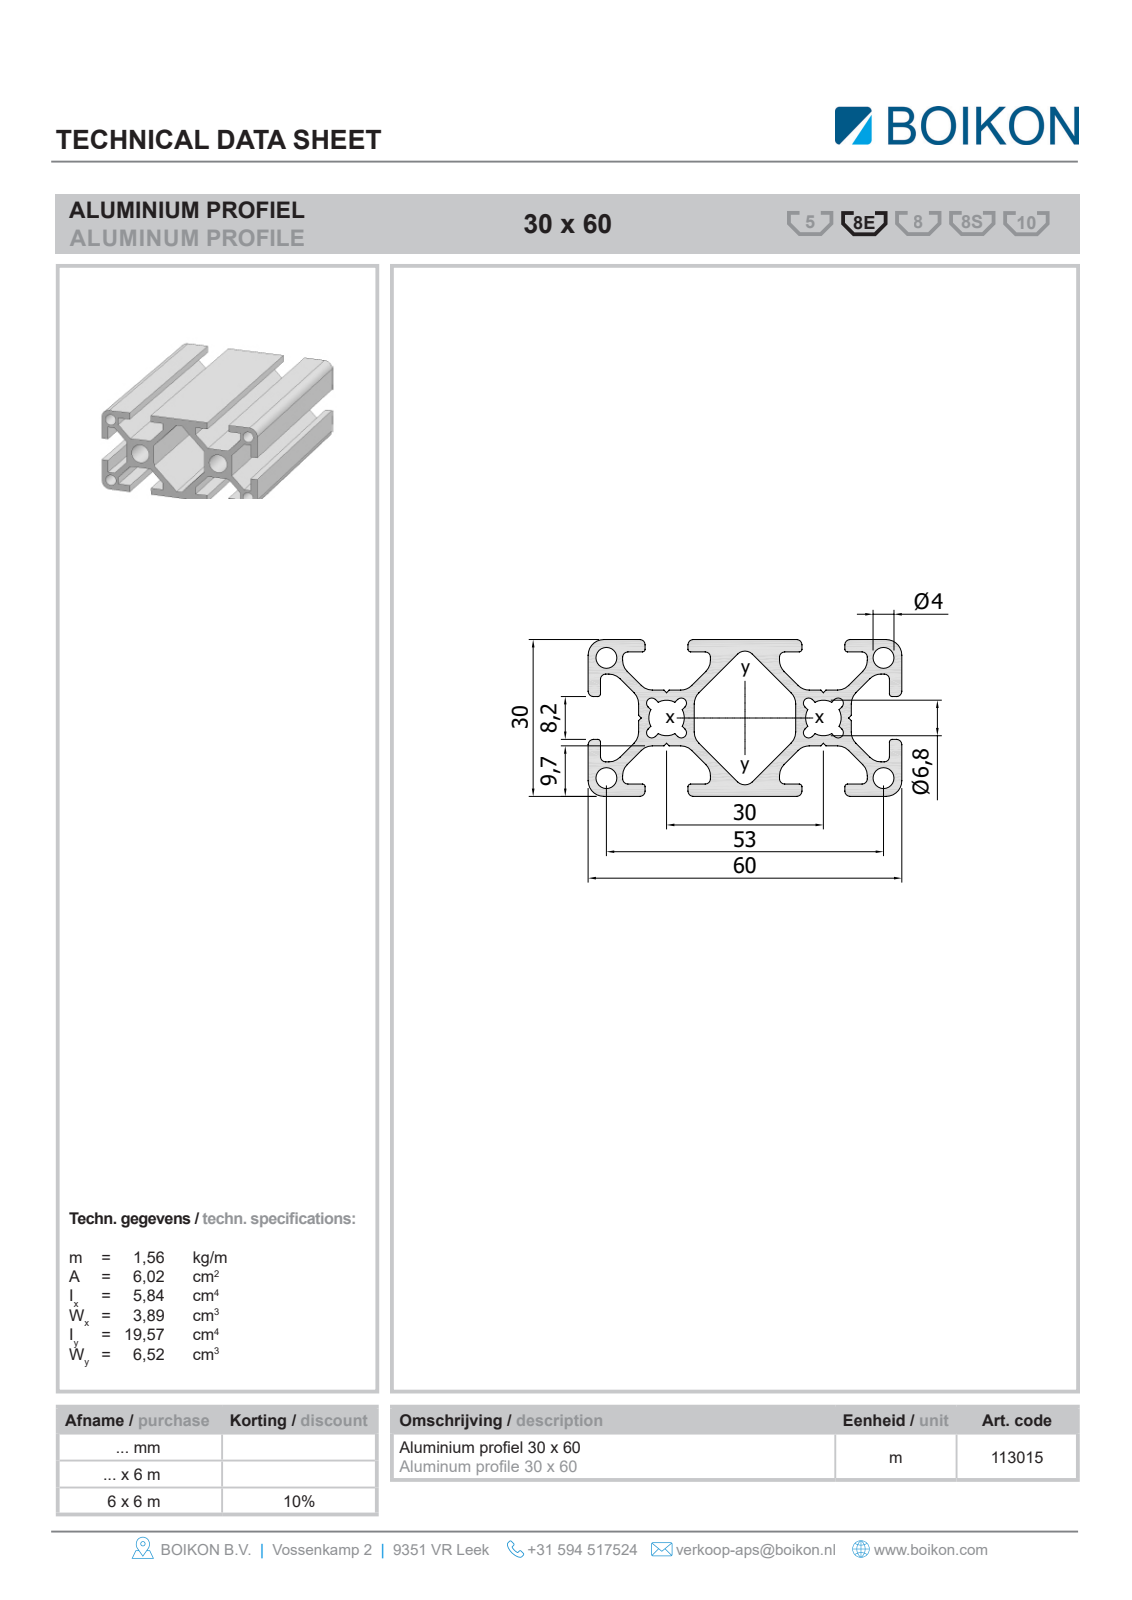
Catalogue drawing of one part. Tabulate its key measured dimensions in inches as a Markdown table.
| quantity | value |
| --- | --- |
| part name | Root; 11301530x60BOIKON0 |
| STEP written by | HiCAD 2013 1802.4 Build 509 (AUTOMOTIVE_DESIGN) |
| units | inches |
| bodies | 1 solid, 84 faces (74 planar, 10 cylindrical, 0 other) |
| overall size | 39.37 × 2.362 × 1.181 |
| volume | 36.26 in³ |
| surface area | 820.1 in² |
| round holes (diameter × count) | 0.157 × 4, 0.268 × 2 |
| partial cylindrical surfaces (radius × count) | 0.118 × 4 |
| main face-to-face distances | 1.181, 0.094, 0.079, 0.835, 0.799, 0.705, 0.382, 0.287, 1.087, 0.756 |
| hole center spacings | 0.64, 1.695, 0.906, 2.087, 2.275, 1.181 |
